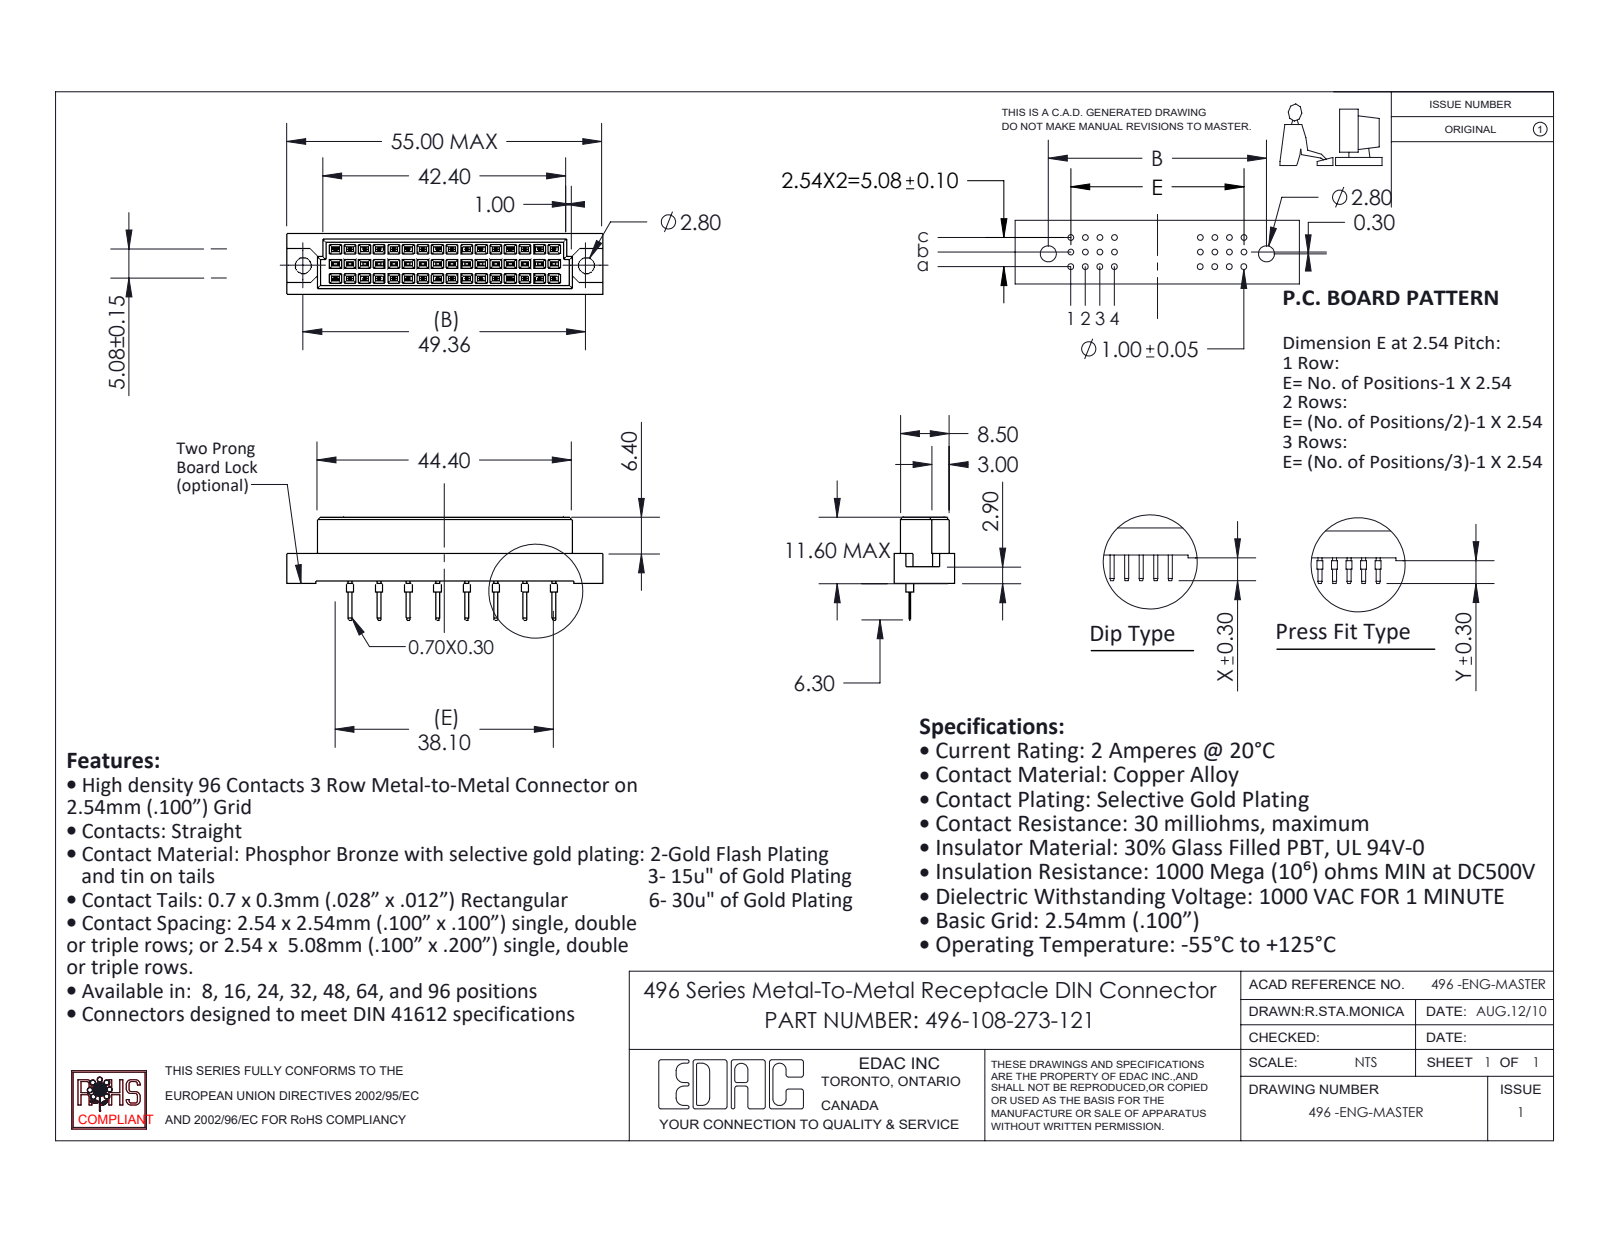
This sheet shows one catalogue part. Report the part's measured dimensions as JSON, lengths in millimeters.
{"part_name": "496-108-273-121; 496 Part_48; 496-290_73", "step_written_by": "SolidWorks 2020 (CONFIG_CONTROL_DESIGN)", "units": "millimeters", "bodies": {"solids": 9, "faces": 810, "planar": 790, "cylindrical": 20, "other": 0}, "overall_size": [55, 17.9, 10.6], "volume_mm3": 4615, "surface_area_mm2": 4417, "round_holes": [[2.8, 2]], "round_bosses_or_shafts": [[1, 8]], "face_to_face_distances": [2.54, 5.08, 1.05, 9.55, 0.81, 10.6, 3.35, 1.73, 8.5, 0.56], "hole_center_spacings": [49.36]}
